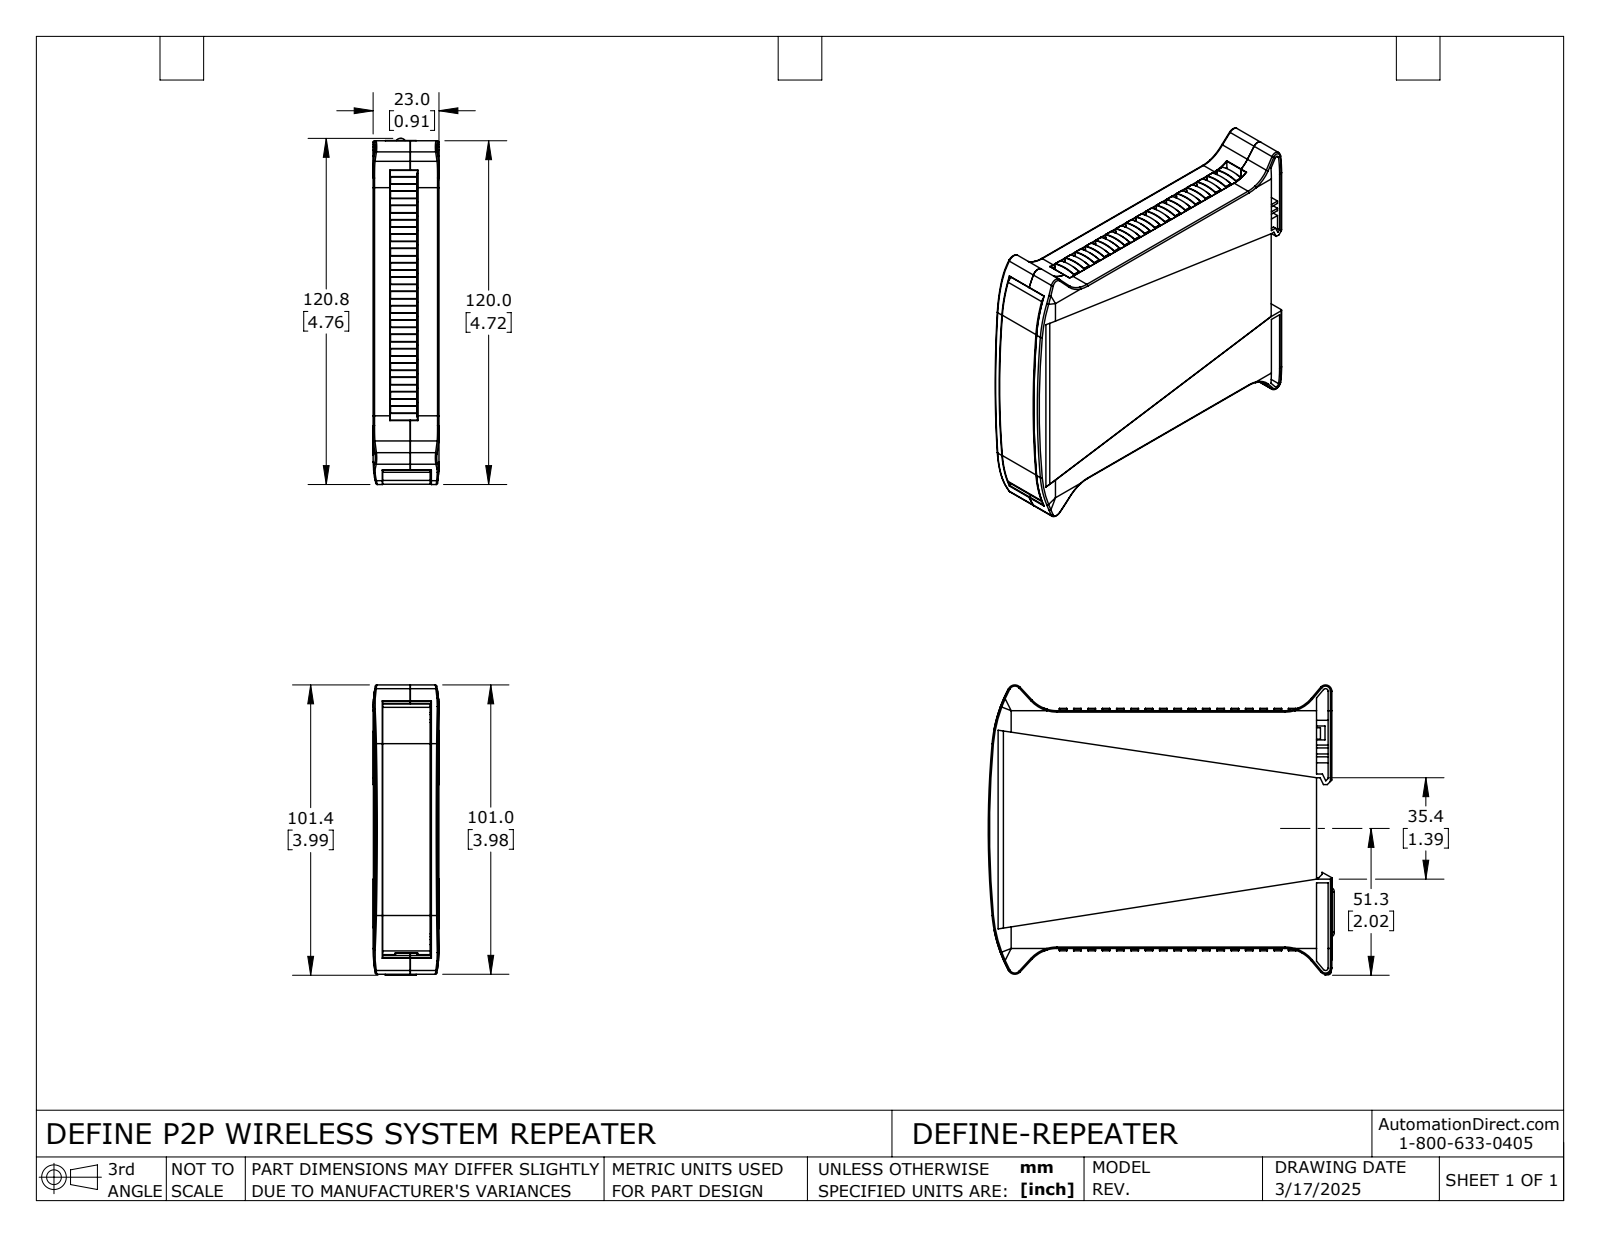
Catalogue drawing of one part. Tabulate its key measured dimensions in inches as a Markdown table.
| quantity | value |
| --- | --- |
| part name | DEFINE-REPEATER |
| STEP written by | SolidWorks 2024 (AUTOMOTIVE_DESIGN) |
| units | inches |
| bodies | 7 solids, 1721 faces (1207 planar, 332 cylindrical, 182 other) |
| overall size | 4.757 × 3.99 × 0.906 |
| volume | 3.092 in³ |
| surface area | 111.6 in² |
| round holes (diameter × count) | 0.118 × 4, 0.075 × 1, 0.146 × 1, 0.241 × 1 |
| round bosses / shafts (diameter × count) | 0.089 × 1 |
| partial cylindrical surfaces (radius × count) | 0.01 × 15, 0.02 × 11, 0.006 × 10, 0.004 × 4, 0.039 × 4, 0.472 × 4, 1.893 × 4, 0.079 × 3 |
| main face-to-face distances | 0.778, 0.055, 0.902, 0.065, 0.833, 0.898, 0.843, 0.069, 0.059, 0.837 |
| hole center spacings | 4.058, 5.368, 0.268, 0.739, 3.268, 3.546, 3.78, 4.175 |
